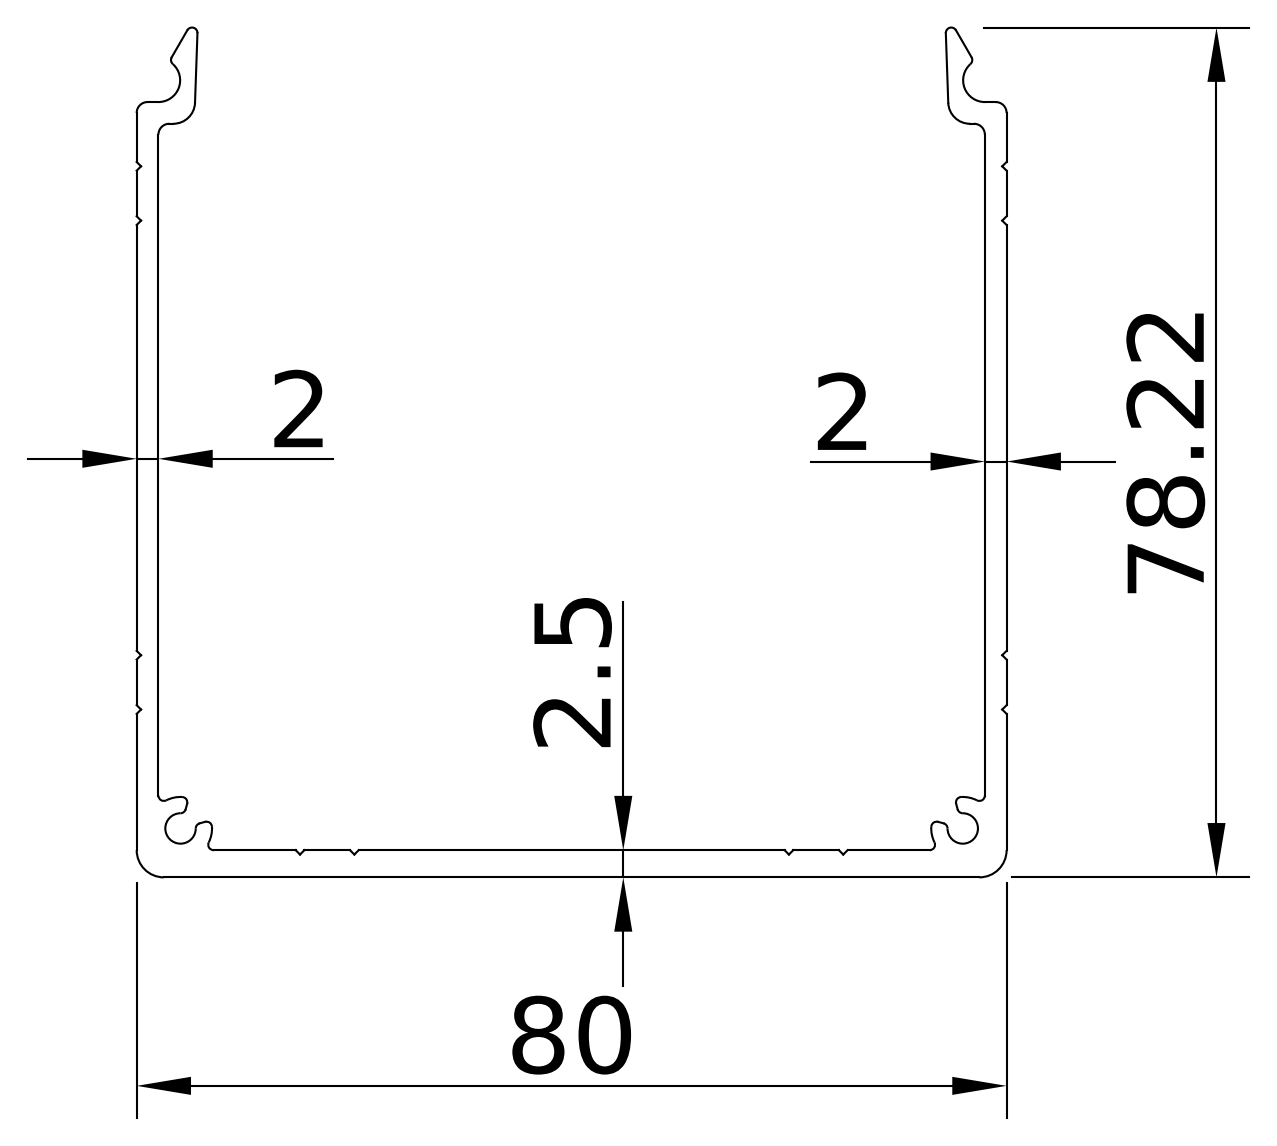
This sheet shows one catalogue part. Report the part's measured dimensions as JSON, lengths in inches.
{"part_name": "BPRCA0000016", "step_written_by": "Autodesk Inventor 2022 (AUTOMOTIVE_DESIGN)", "units": "inches", "bodies": {"solids": 1, "faces": 88, "planar": 56, "cylindrical": 32, "other": 0}, "overall_size": [3.937, 3.152, 3.08], "volume_in3": 3.236, "surface_area_in2": 77.45, "partial_cylinders_radius": [[0.02, 16], [0.039, 4], [0.079, 4], [0.055, 2], [0.098, 2], [0.114, 2]], "face_to_face_distances": [0.079, 3.074, 3.153, 0.098, 2.995, 3.937, 0.036, 0.139, 0.139, 1.113]}
